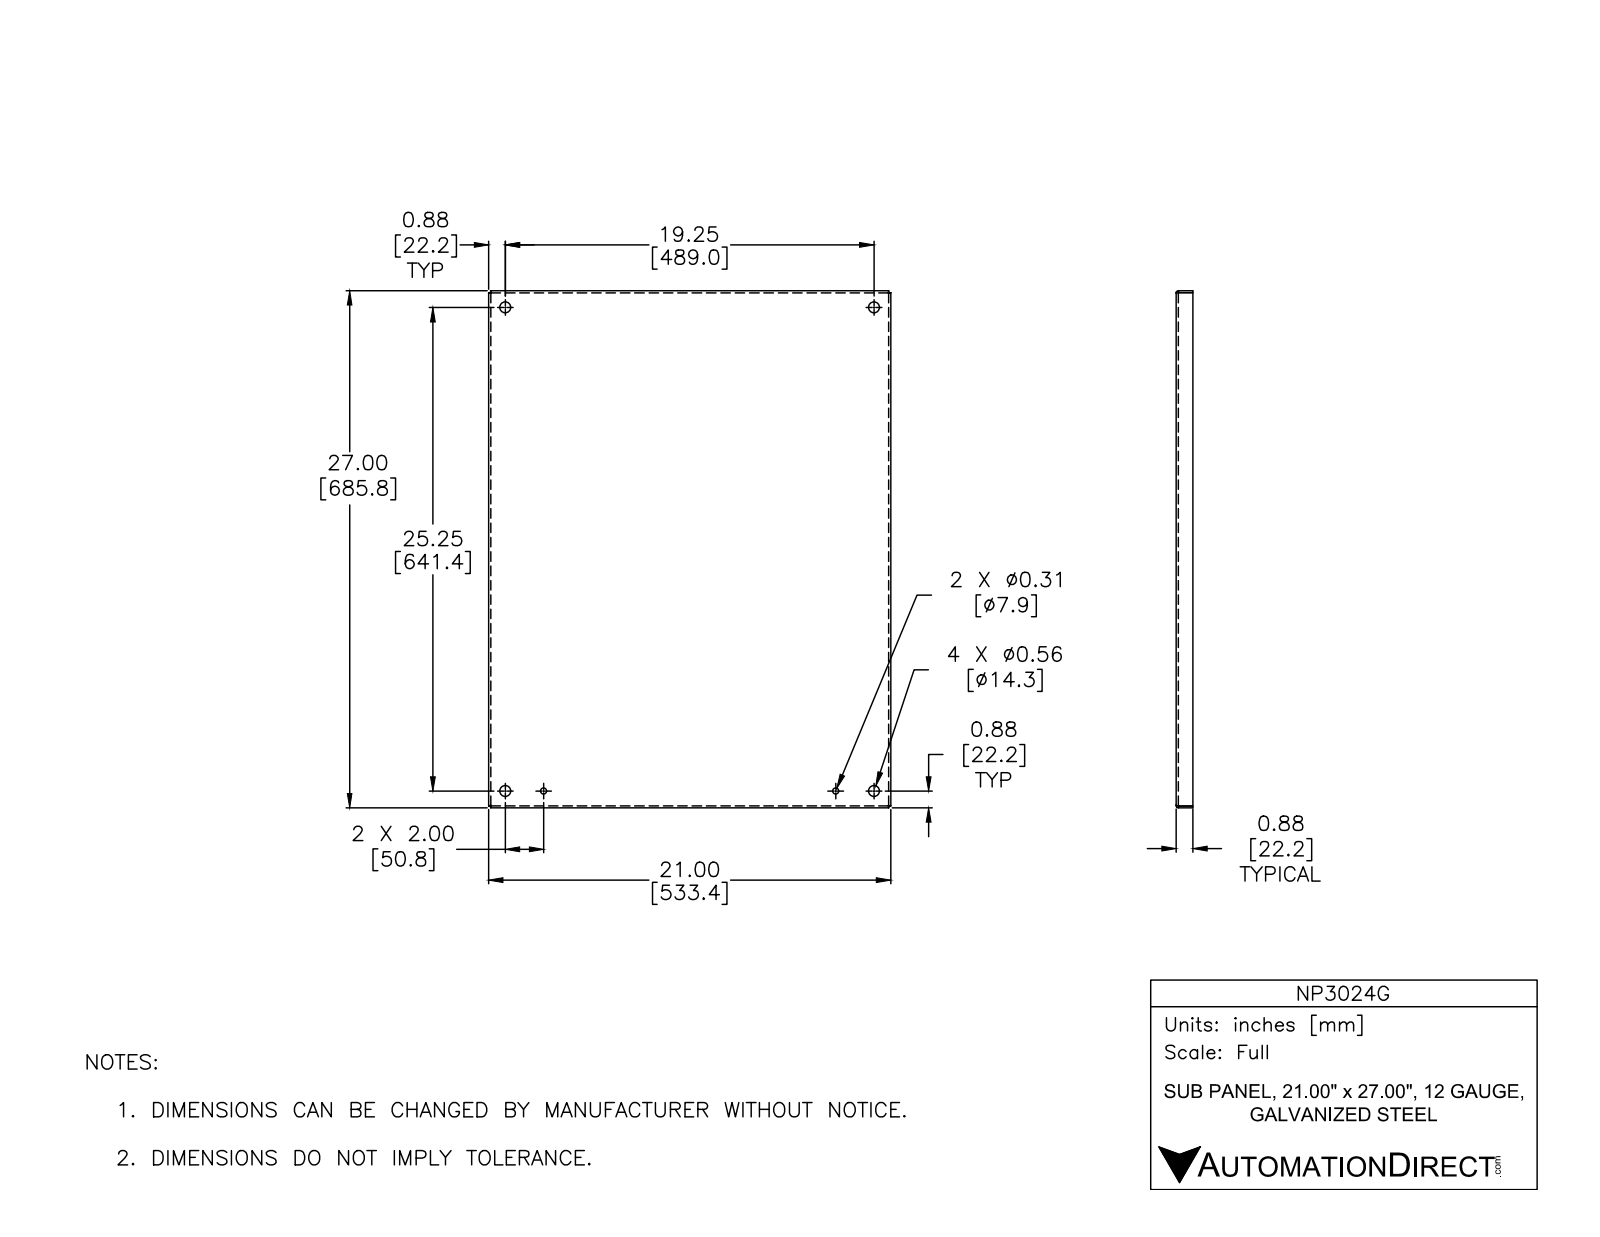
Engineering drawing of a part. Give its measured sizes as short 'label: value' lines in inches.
name: NP3024G
written by: Autodesk Inventor 2012 (AUTOMOTIVE_DESIGN)
unit: in
bodies: 1 solid, 44 faces (22 planar, 14 cylindrical, 8 other)
size: 27 × 21 × 0.875
volume: 59.68 in³; area: 1 284 in²
holes: 4× ⌀0.563, 2× ⌀0.312
rounds: 4× R0.031, 4× R0.125
face distances: 0.094, 20.906, 26.906, 21, 20.813, 27, 26.813, 0.781, 0.875, 0.105
hole spacings: 19.25, 25.25, 25.329, 31.751, 2, 2, 15.25, 17.25
